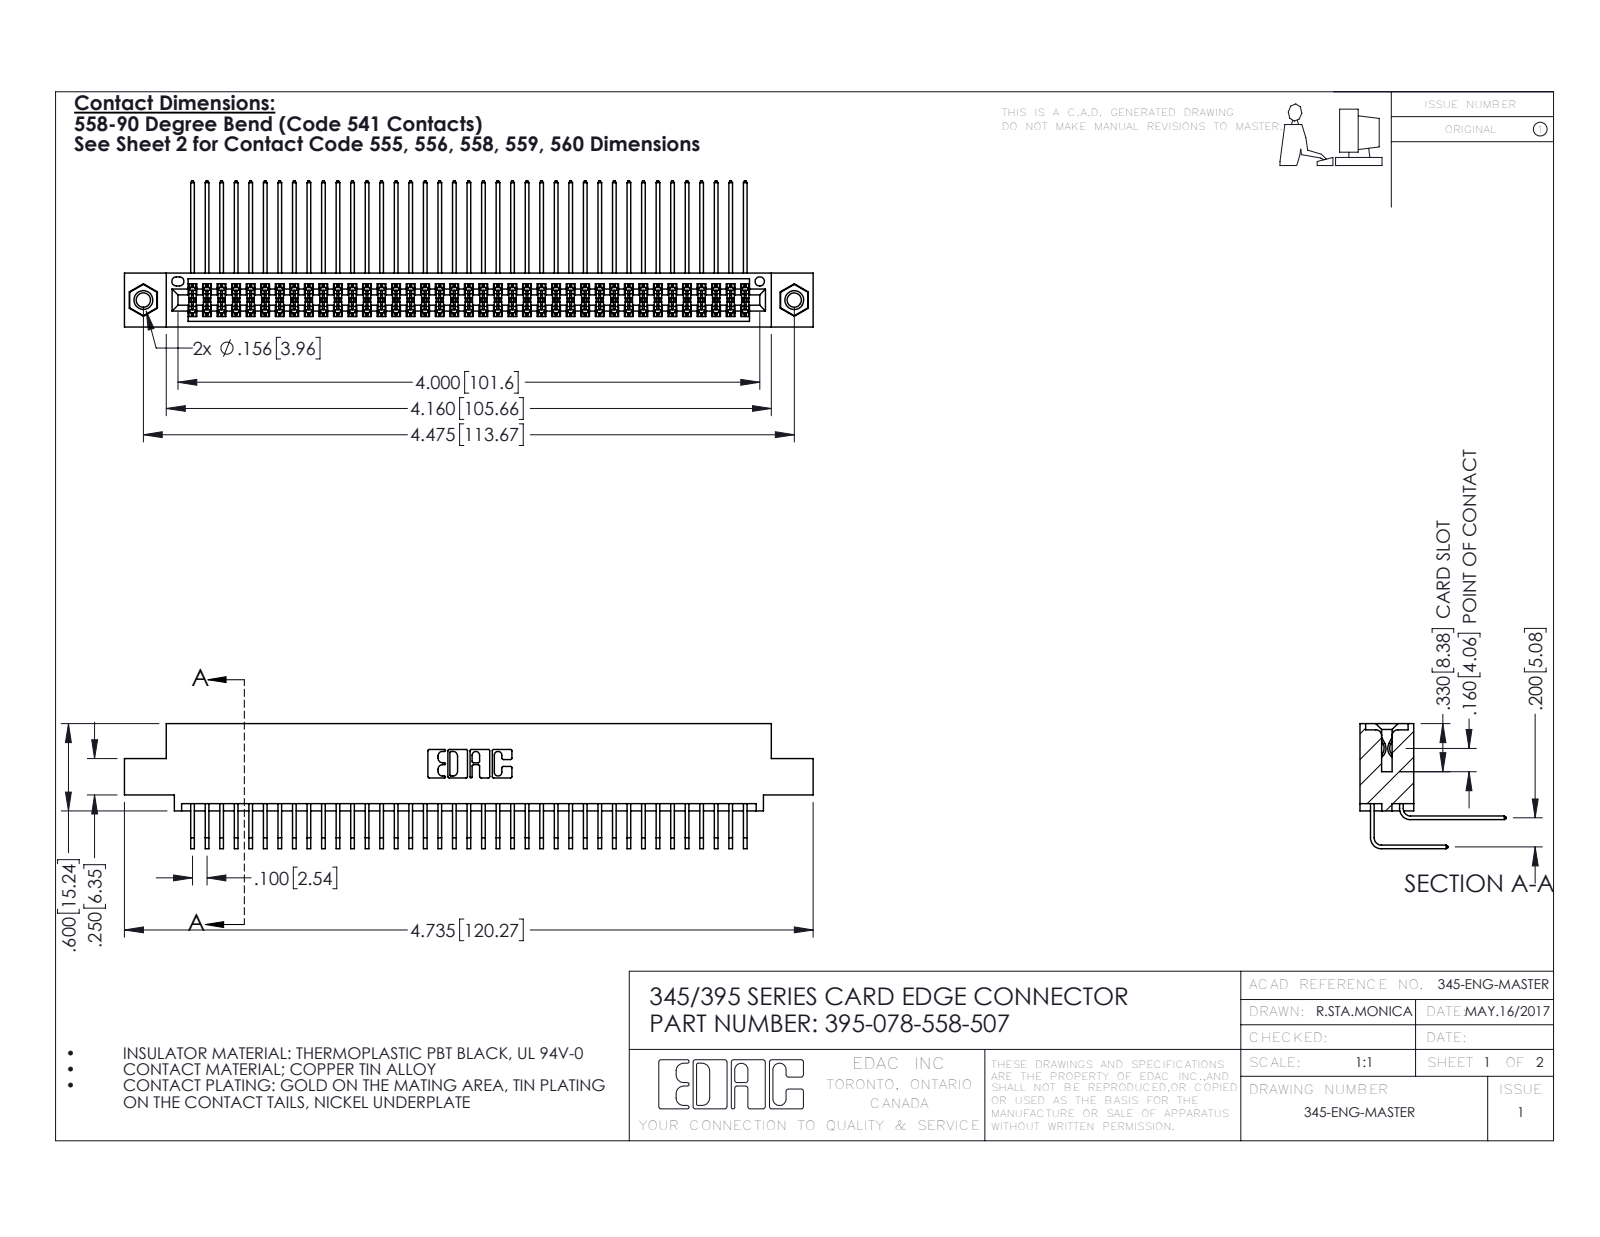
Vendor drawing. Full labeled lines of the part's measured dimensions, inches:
Part name (STEP PRODUCT): 395-078-558-507; 345-250-001_345-250-005-103; 345-292-001_558 Tail - 2; 345 Part_0.110 Offset - 0.156 Dia-TI (+1 more)
STEP written by: SolidWorks 2016 (CONFIG_CONTROL_DESIGN)
Units: inches
Bodies: 81 solids, 4246 faces (2846 planar, 1384 cylindrical, 16 other)
Overall size (bounding box): 4.735 × 1.005 × 0.859
Volume: 0.733 in³ · Surface area: 30.91 in²
Round holes (diameter × count): ⌀0.098 ×2, ⌀0.125 ×2, ⌀0.156 ×2, ⌀0.064 ×1
Round bosses / shafts (diameter × count): ⌀0.155 ×2
Partial cylindrical surfaces — rounded edges, fillets, slot ends (radius × count): R0.006 ×118, R0.01 ×22, R0.007 ×6, R0.031 ×6, R0.026 ×3, R0.014 ×2, R0.019 ×2, R0.022 ×2
Main face-to-face distances: 0.072, 0.298, 0.2, 0.37, 0.098, 0.272, 0.025, 0.225, 0.025, 0.175
Hole centre spacings: 0.27, 4.239, 4.475
